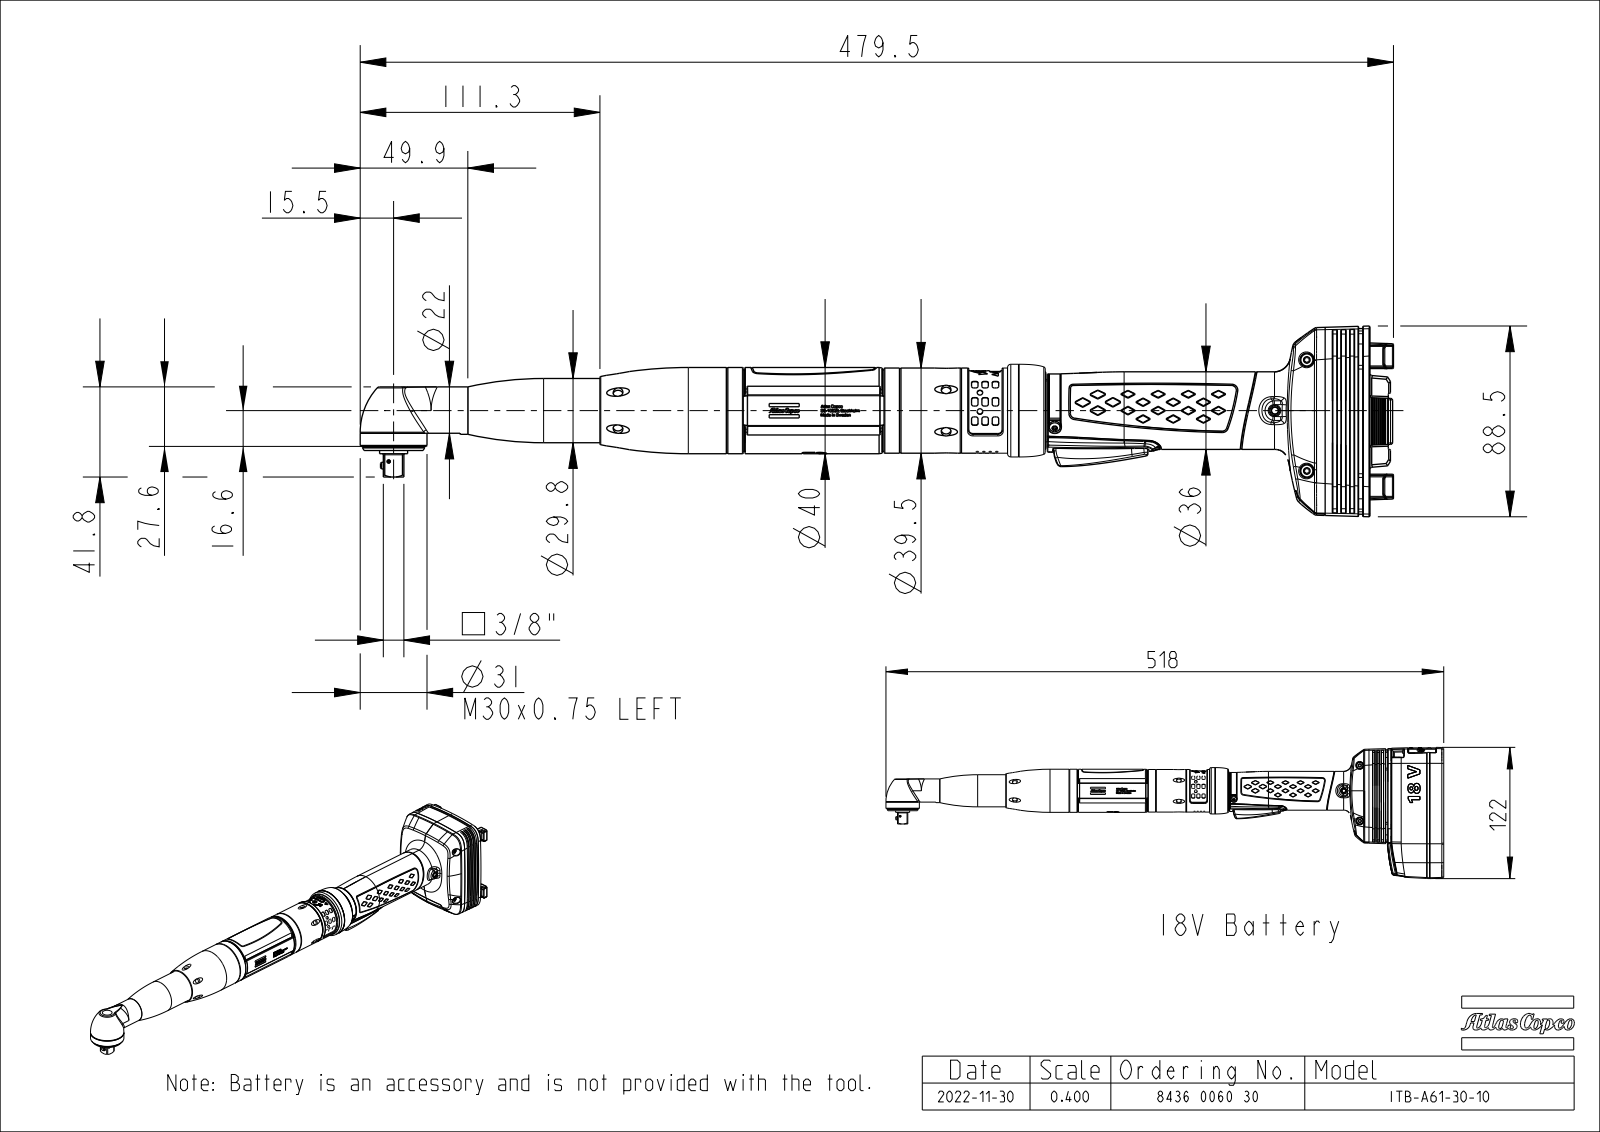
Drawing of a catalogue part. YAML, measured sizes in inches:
part_name: "EXT_COMP_SW0037"
step_written_by: "CREO PARAMETRIC BY PTC INC, 2020281 (CONFIG_CONTROL_DESIGN)"
units: inches
bodies: {solids: 1, faces: 4730, planar: 1423, cylindrical: 956, other: 2351}
overall_size: [18.898, 3.484, 2.935]
volume: 39.45
surface_area: 146.8
round_holes:
  - {diameter: 0.039, count: 12}
  - {diameter: 0.177, count: 6}
  - {diameter: 0.11, count: 4}
  - {diameter: 0.063, count: 2}
  - {diameter: 0.197, count: 2}
  - {diameter: 0.049, count: 1}
  - {diameter: 0.059, count: 1}
  - {diameter: 0.126, count: 1}
  - {diameter: 0.138, count: 1}
  - {diameter: 0.154, count: 1}
  - {diameter: 0.186, count: 1}
  - {diameter: 0.472, count: 1}
round_bosses_or_shafts:
  - {diameter: 0.22, count: 2}
  - {diameter: 1.693, count: 1}
  - {diameter: 1.575, count: 1}
  - {diameter: 1.555, count: 1}
  - {diameter: 1.417, count: 1}
  - {diameter: 1.22, count: 1}
  - {diameter: 1.173, count: 1}
  - {diameter: 1.134, count: 1}
partial_cylinders:
  - {radius: 0.02, count: 106}
  - {radius: 0.039, count: 56}
  - {radius: 0.012, count: 37}
  - {radius: 0.008, count: 28}
  - {radius: 0.079, count: 26}
  - {radius: 0.009, count: 18}
  - {radius: 0.016, count: 18}
  - {radius: 0.011, count: 12}
face_to_face_distances: [0.199, 0.079, 0.157, 0.236, 0.315, 0.413, 0.717, 0.016, 0.266, 1.329]
hole_center_spacings: [0.118, 0.236, 0.384, 0.543, 0.354, 6.014, 0.768, 4.119]
